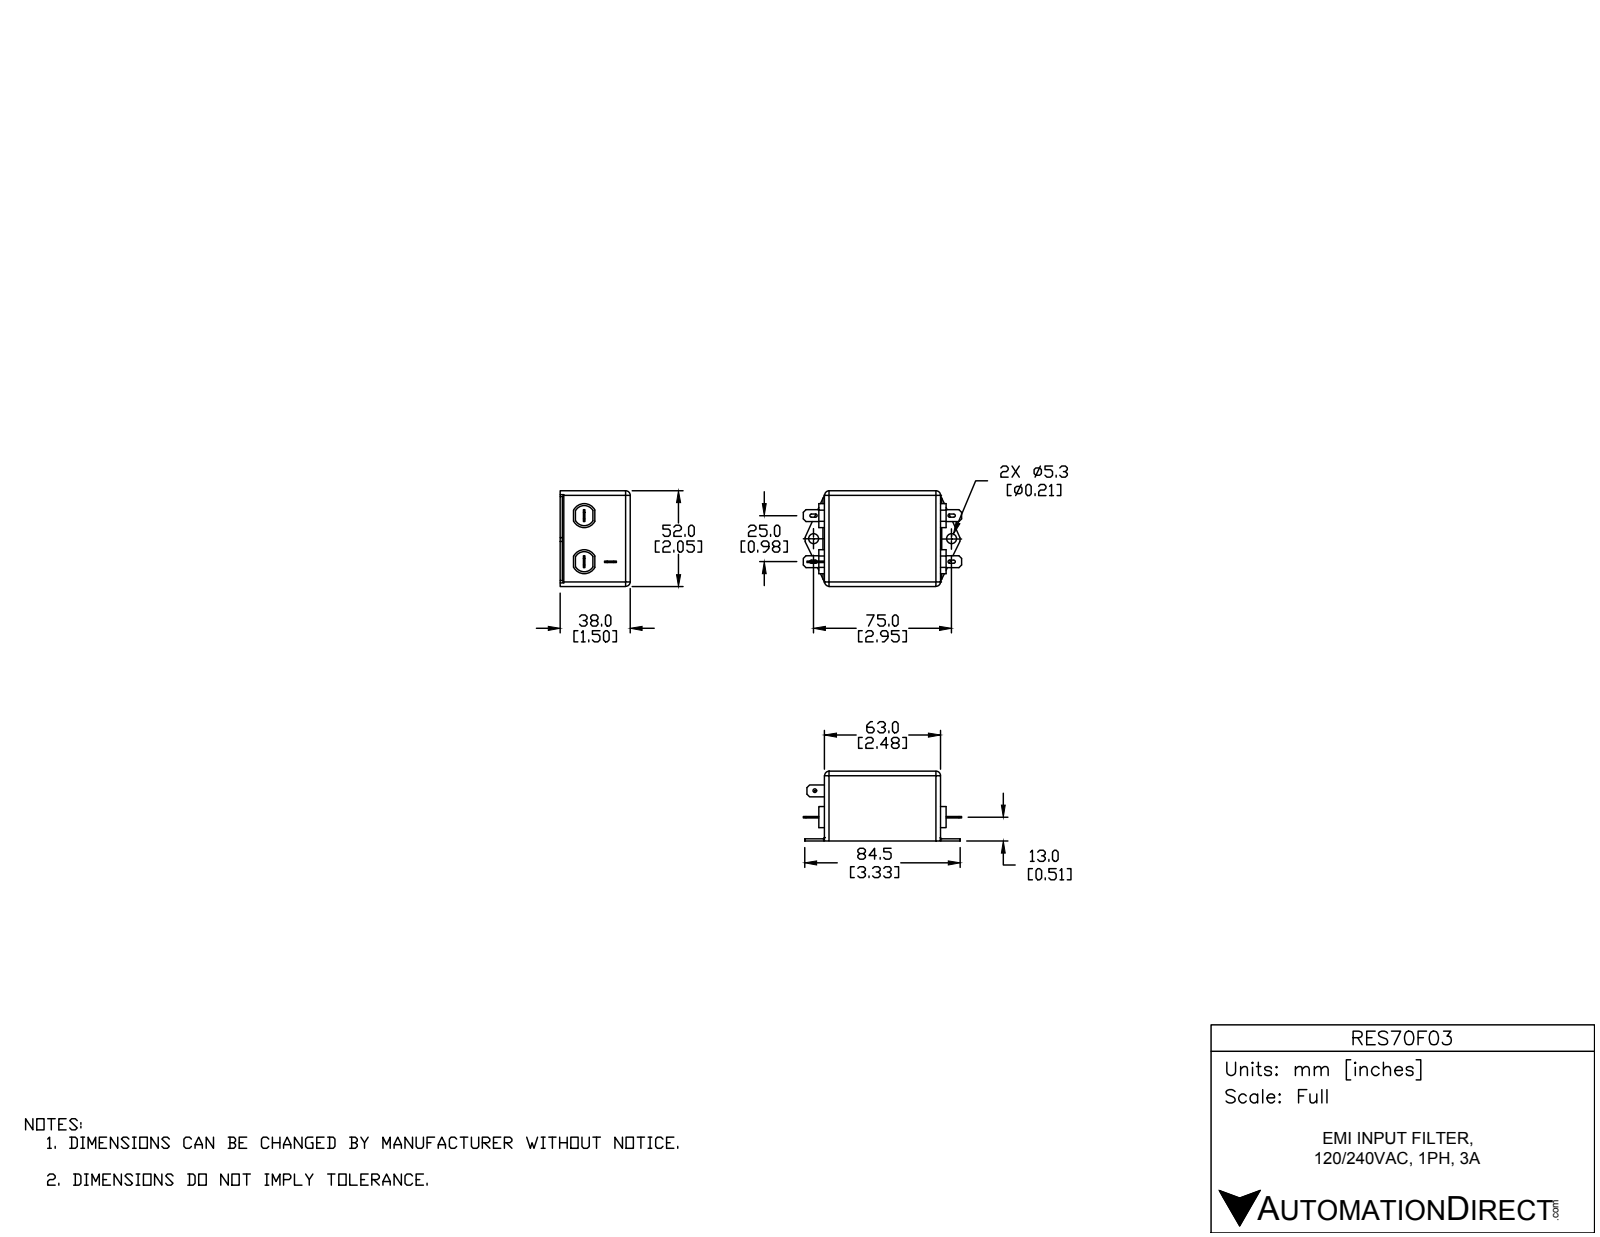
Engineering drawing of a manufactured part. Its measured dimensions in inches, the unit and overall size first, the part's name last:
Units: inches
Overall size (bounding box): 3.386 × 2.067 × 1.161
Round holes (diameter × count): ⌀0.209 ×2, ⌀0.079 ×1
Partial cylindrical surfaces — rounded edges, fillets, slot ends (radius × count): R0.098 ×10, R0.035 ×8, R0.03 ×2, R0.217 ×2, R0.256 ×2
Main face-to-face distances: 1.161, 2.067, 2.48, 0.059, 0.047, 1.114, 2.539, 2.598, 0.031, 0.409
Hole centre spacings: 2.953
Volume: 6.036 in³ · Surface area: 23.85 in²
Bodies: 1 solid, 133 faces (79 planar, 50 cylindrical, 4 other)
Part name (STEP PRODUCT): RES70F03
STEP written by: SolidWorks 2015 (AUTOMOTIVE_DESIGN)
